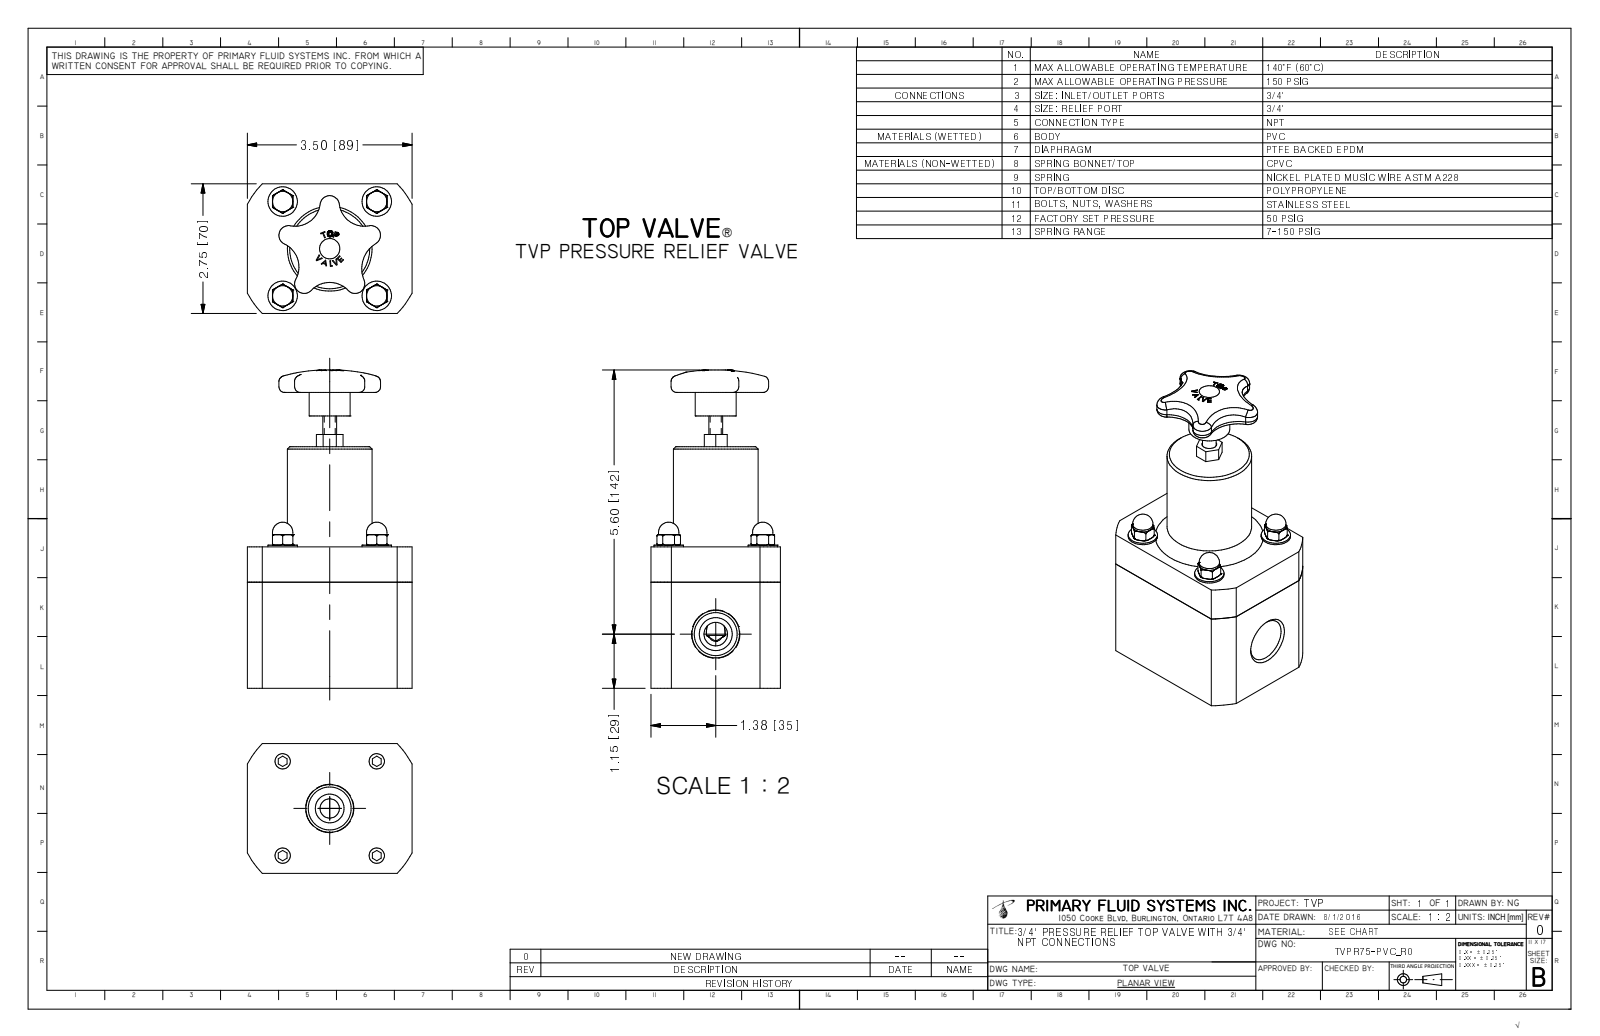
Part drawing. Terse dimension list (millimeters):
name: TVPR75-PVC_R0
written by: Autodesk Inventor 2009 (AUTOMOTIVE_DESIGN)
unit: mm
bodies: 1 solid, 304 faces (123 planar, 44 cylindrical, 137 other)
size: 171.5 × 88.9 × 69.9
volume: 552 700 mm³; area: 55 460 mm²
holes: 4× ⌀4.4, 2× ⌀23.1, 1× ⌀61
bosses: 4× ⌀15.9, 4× ⌀11, 1× ⌀60.3, 1× ⌀45.7, 1× ⌀22.1, 1× ⌀7.4
rounds: 5× R2.2, 5× R5.2, 4× R13.6, 4× R16.7, 1× R15.9, 1× R18.9, 1× R50.5
face distances: 69.9, 88.9, 76.2, 130.2, 54, 19.1, 69.9, 50.8, 15.2, 61
hole spacings: 35.9, 50.8, 71.8
